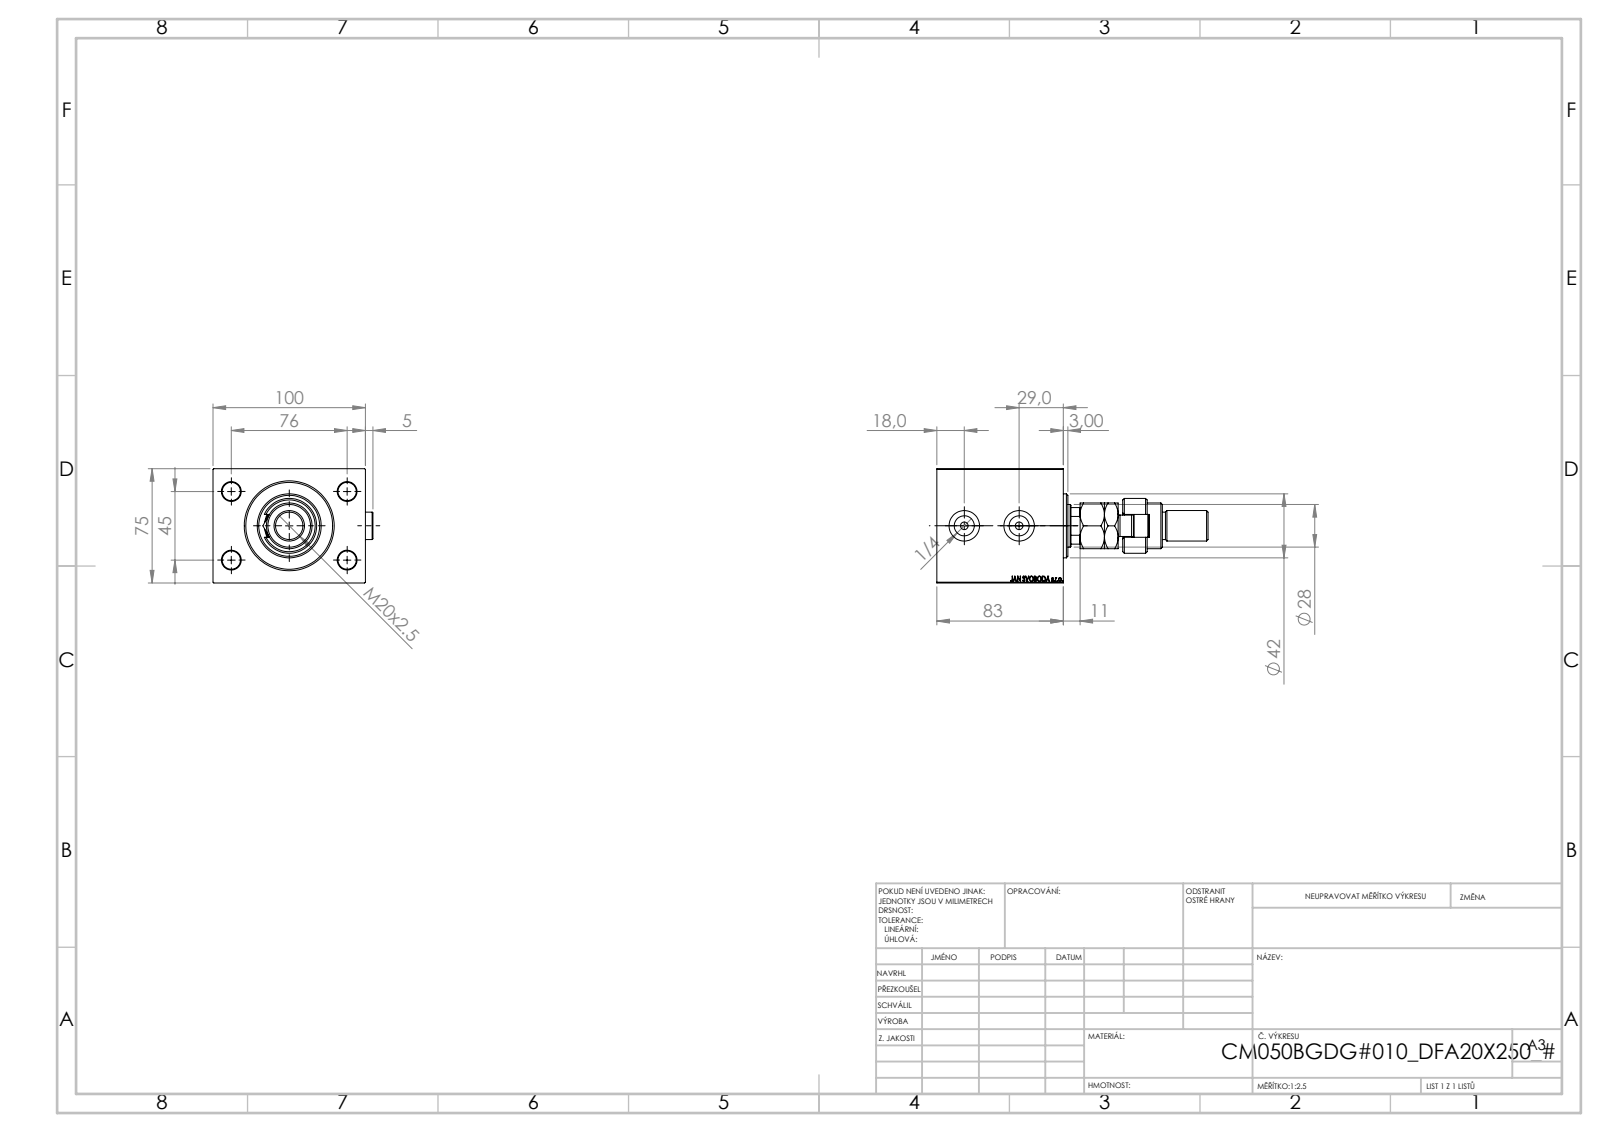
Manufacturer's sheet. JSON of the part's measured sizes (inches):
{"part_name": "MFA; V450CM_B_VCP; Zatka_OIL_PORT; V450CM_B_Body (+2 more)", "step_written_by": "SolidWorks 2019 (CONFIG_CONTROL_DESIGN)", "units": "inches", "bodies": {"solids": 7, "faces": 1021, "planar": 464, "cylindrical": 83, "other": 474}, "overall_size": [7.008, 4.13, 2.953], "volume_in3": 38.61, "surface_area_in2": 153.4, "round_holes": [[0.472, 4], [0.197, 2], [0.518, 2], [0.787, 2], [0.728, 1], [1.102, 1], [1.24, 1], [1.28, 1], [1.969, 1], [2.047, 1], [2.244, 1]], "round_bosses_or_shafts": [[0.709, 3], [1.654, 1], [1.417, 1], [1.181, 1], [0.866, 1], [0.787, 1], [0.551, 1]], "partial_cylinders_radius": [[0.295, 1], [0.472, 1], [0.531, 1]], "face_to_face_distances": [2.953, 3.937, 3.268, 2.008, 1.26, 0.394, 1.181, 0.85, 1.157, 2.417], "hole_center_spacings": [1.739, 1.772, 2.992, 3.477, 1.417]}
